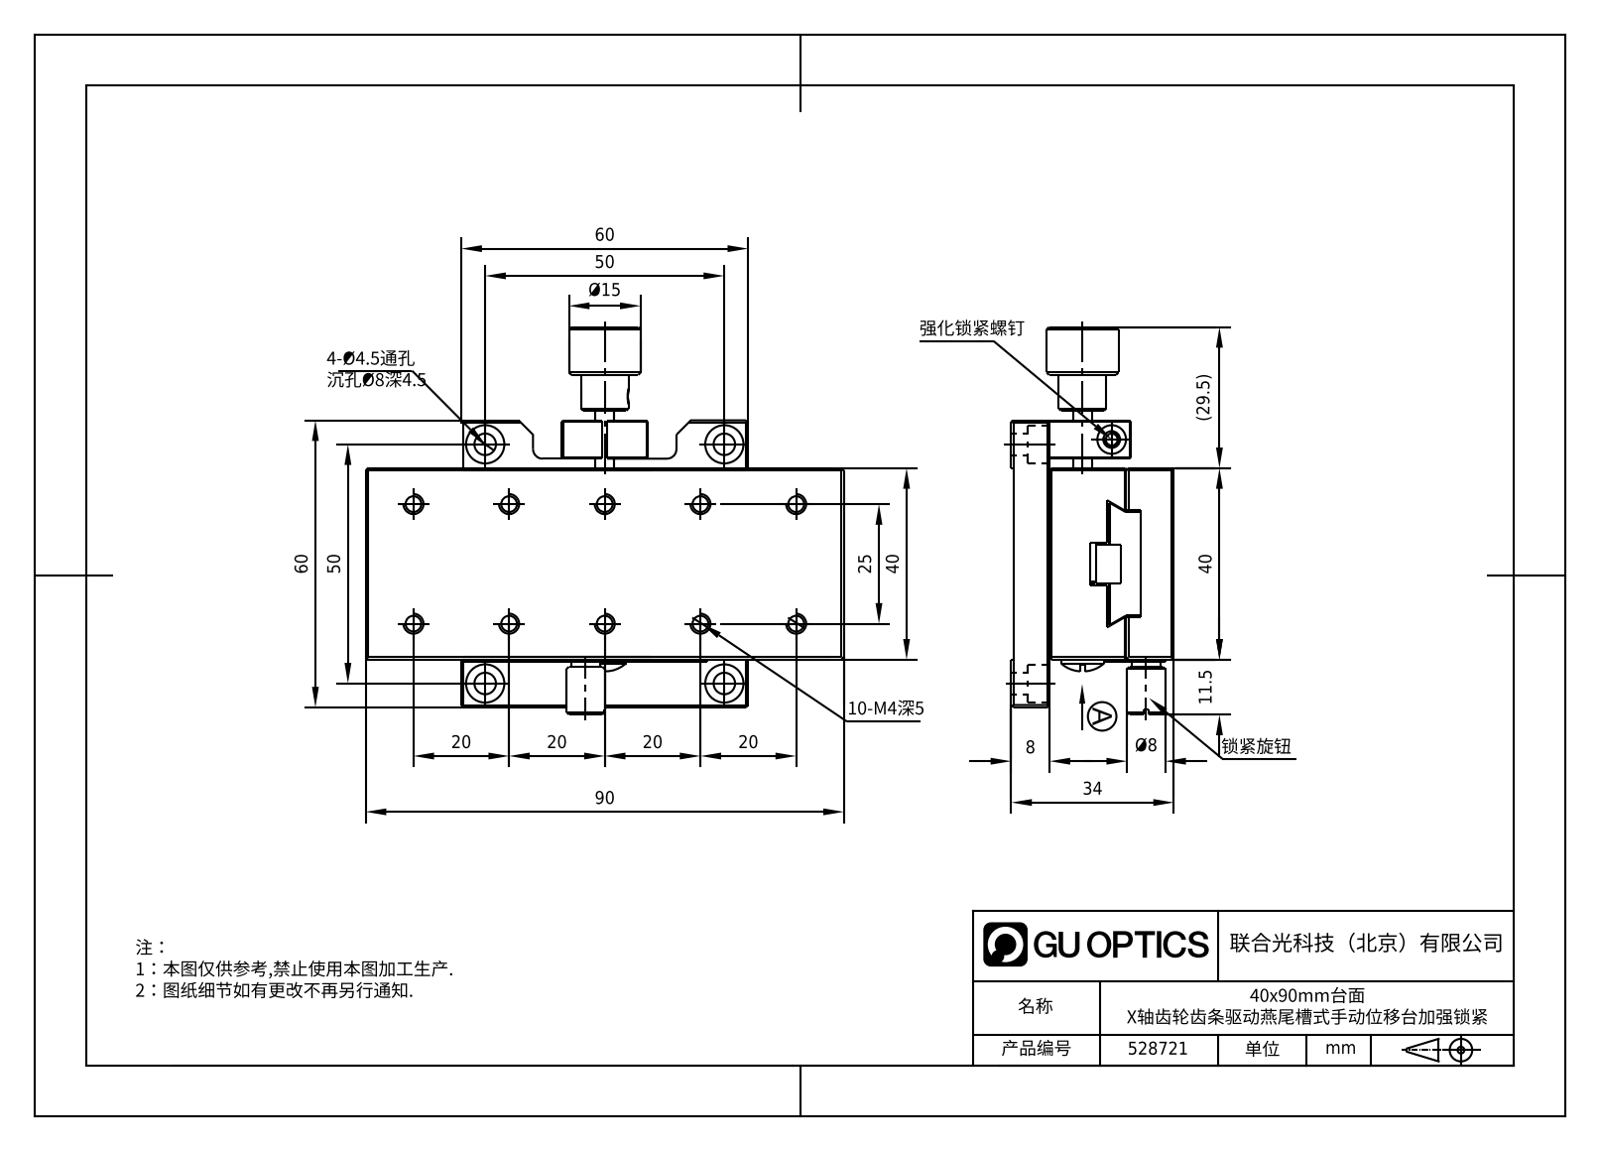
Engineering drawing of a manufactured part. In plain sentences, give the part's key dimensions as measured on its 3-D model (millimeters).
The part is named "528721". Its 3-D file was written by "SolidWorks 2020 (CONFIG_CONTROL_DESIGN)". It is 6 solids with 552 faces: 309 planar, 75 cylindrical and 168 other. Overall it measures 90 by 80.51 by 34 millimeters. Its volume is 120 073 cubic millimeters and its surface area 47 434 square millimeters. Round holes: 12 of diameter 3.24, 6 of diameter 8, 5 of diameter 2.8, 5 of diameter 5, 4 of diameter 2.01, 4 of diameter 4.5, 4 of diameter 6, 3 of diameter 2.46, 3 of diameter 3.5, 2 of diameter 1.57, 2 of diameter 2.2, 2 of diameter 4.2. Round bosses or shafts: 2 of diameter 8, 1 of diameter 9, 1 of diameter 6.5, 1 of diameter 6, 1 of diameter 5.83, 1 of diameter 4, 1 of diameter 3. Partial cylindrical surfaces (rounded edges, fillets, slot ends): 6 of radius 2, 2 of radius 1.8. The main face-to-face distances are 7, 26, 19, 16, 0.5, 10, 7.5, 3, 26.5, 4. The hole center spacings are 20, 27.95, 32.02, 45.07, 25, 40, 47.17, 12.5.
